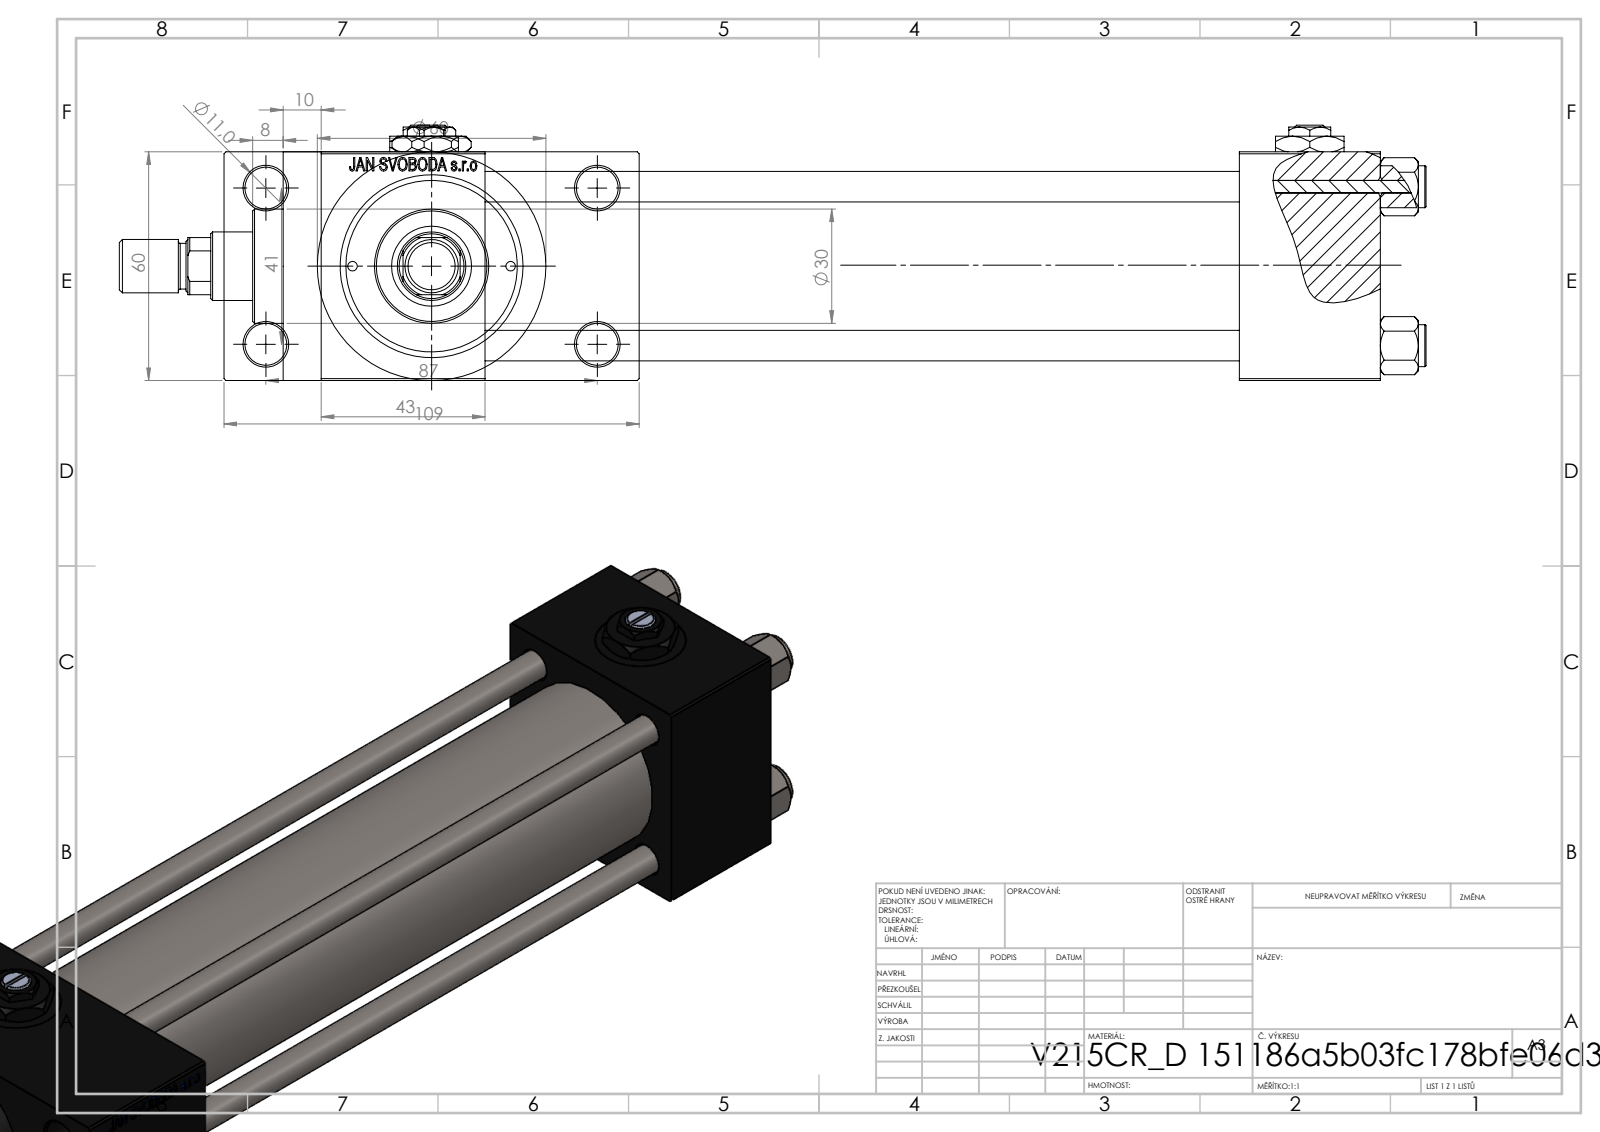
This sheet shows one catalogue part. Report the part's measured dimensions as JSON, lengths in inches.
{"part_name": "NUT_M5_D; V215CR_D_TYCINKA; V215CR_D_Body; ROD_END_AH (+3 more)", "step_written_by": "SolidWorks 2019 (CONFIG_CONTROL_DESIGN)", "units": "inches", "bodies": {"solids": 14, "faces": 1227, "planar": 552, "cylindrical": 107, "other": 568}, "overall_size": [13.504, 4.291, 2.638], "volume_in3": 38.65, "surface_area_in2": 288.4, "round_holes": [[0.315, 4], [0.433, 4], [0.656, 4], [0.945, 4], [0.276, 3], [0.098, 2], [0.335, 1], [0.709, 1], [0.827, 1], [1.22, 1], [1.575, 1], [1.772, 1]], "round_bosses_or_shafts": [[0.433, 4], [2.362, 1], [1.811, 1], [1.181, 1], [0.551, 1], [0.472, 1]], "partial_cylinders_radius": [[0.335, 1]], "face_to_face_distances": [2.362, 7.795, 0.965, 3.327, 1.457, 9.252, 1.693, 10.945, 9.488, 2.087], "hole_center_spacings": [0.821, 0.892, 1.161, 1.206, 1.642, 1.832, 1.856, 1.893]}
